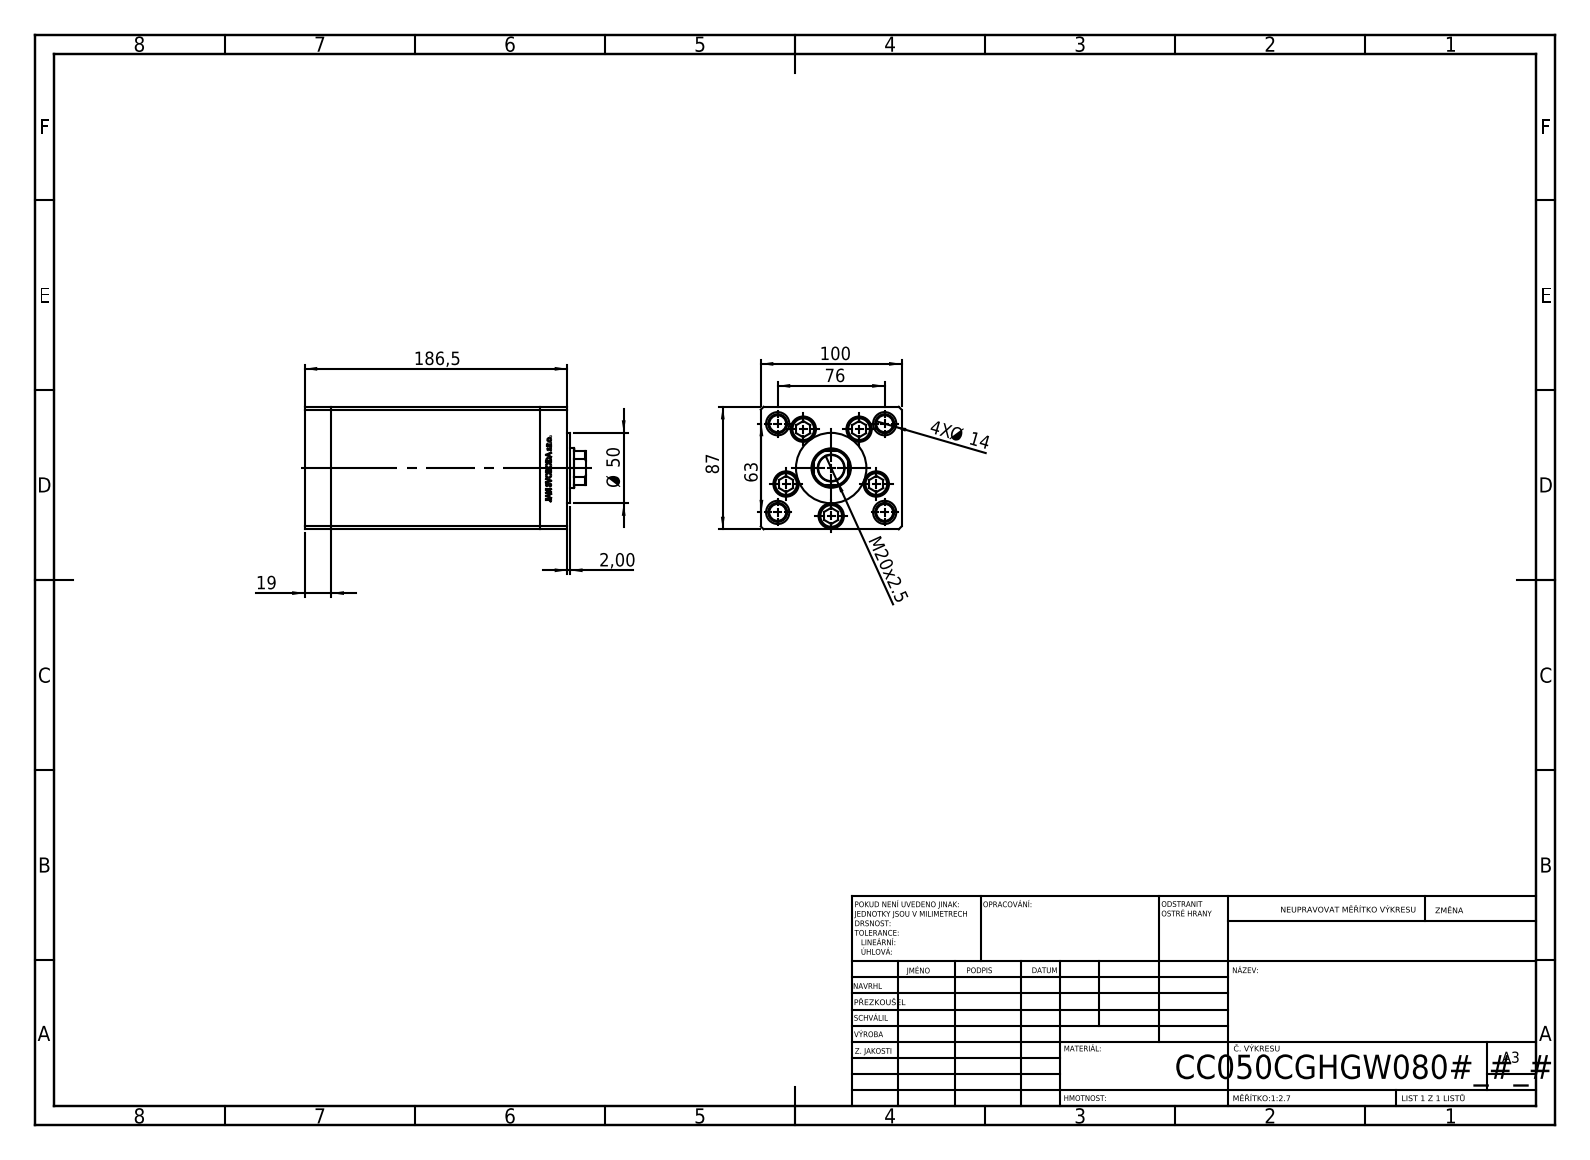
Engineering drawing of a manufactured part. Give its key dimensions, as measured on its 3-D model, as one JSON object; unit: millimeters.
{"part_name": "V220C FRONT; V220C_C MIDDLE; V220C BACK_C; ALLEN BOLT (+1 more)", "step_written_by": "SolidWorks 2019 (CONFIG_CONTROL_DESIGN)", "units": "millimeters", "bodies": {"solids": 13, "faces": 1182, "planar": 544, "cylindrical": 176, "other": 462}, "overall_size": [199.5, 100, 87], "volume_mm3": 1328000, "surface_area_mm2": 230838, "round_holes": [[13.5, 9], [18, 5], [2, 4], [12, 4], [13.16, 4], [16.5, 4], [17, 1], [18.5, 1], [28, 1]], "round_bosses_or_shafts": [[8, 5], [17, 4], [50, 1]], "partial_cylinders_radius": [[0.93, 2], [13.5, 1]], "face_to_face_distances": [100, 87, 19, 148.5, 167.5, 34.25, 186.5, 152.25, 133.25, 15.25], "hole_center_spacings": [34, 49.36, 18.59, 21.03, 38.08, 39.27, 40.83, 43.24]}
